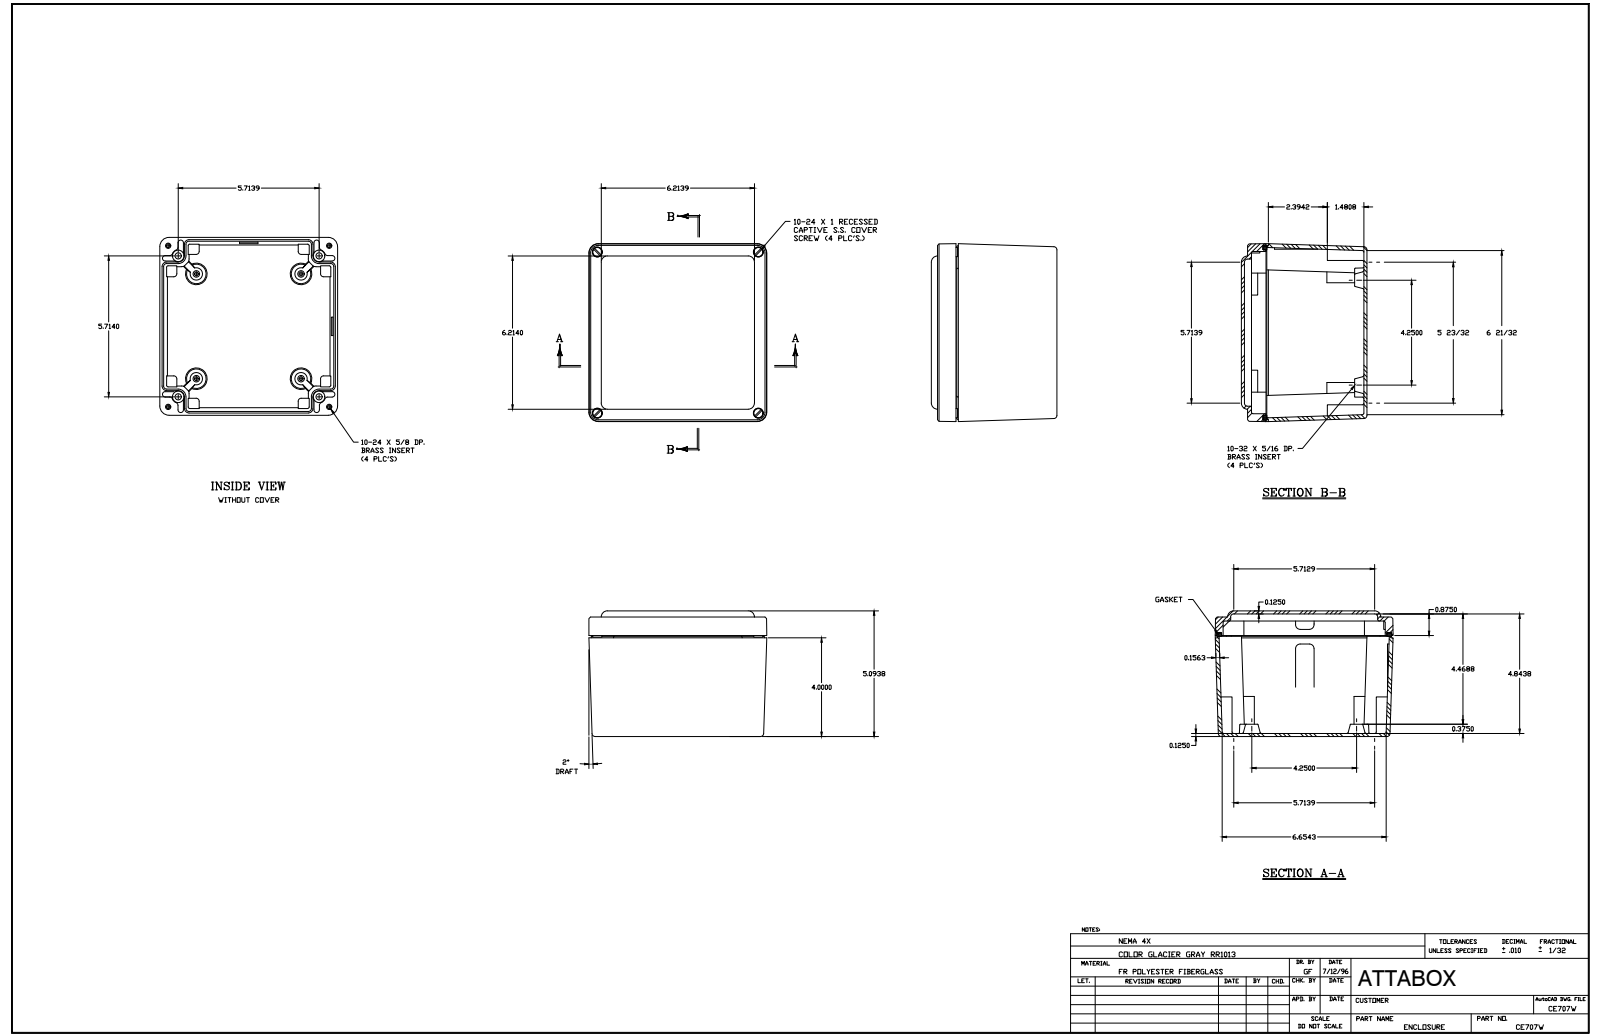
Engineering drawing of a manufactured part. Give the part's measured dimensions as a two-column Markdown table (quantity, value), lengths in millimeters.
| quantity | value |
| --- | --- |
| part name | CE707W |
| STEP written by | SolidWorks 2018 (AUTOMOTIVE_DESIGN) |
| units | millimeters |
| bodies | 23 solids, 1075 faces (423 planar, 260 cylindrical, 392 other) |
| overall size | 183.4 × 183.4 × 129.4 |
| volume | 816 700 mm³ |
| surface area | 354 600 mm² |
| round holes (diameter × count) | 7.1 × 8, 3.7 × 4, 4 × 4, 4 × 4, 4.8 × 4, 5.6 × 4, 5.8 × 4, 7.1 × 4, 8 × 4, 10.3 × 4, 13.5 × 4 |
| round bosses / shafts (diameter × count) | 9.5 × 4, 9.2 × 4, 4.9 × 4 |
| partial cylindrical surfaces (radius × count) | 0.8 × 49, 3.2 × 30, 1.6 × 22, 0.3 × 16, 1.5 × 8, 9.5 × 8, 1.6 × 7, 4.8 × 6 |
| main face-to-face distances | 4.7, 3.2, 123, 129.4, 126.2, 3.2, 126.2, 104, 19.1, 6.4 |
| hole center spacings | 128, 140, 140, 155.9, 156, 165.9, 14.6, 14.6 |
